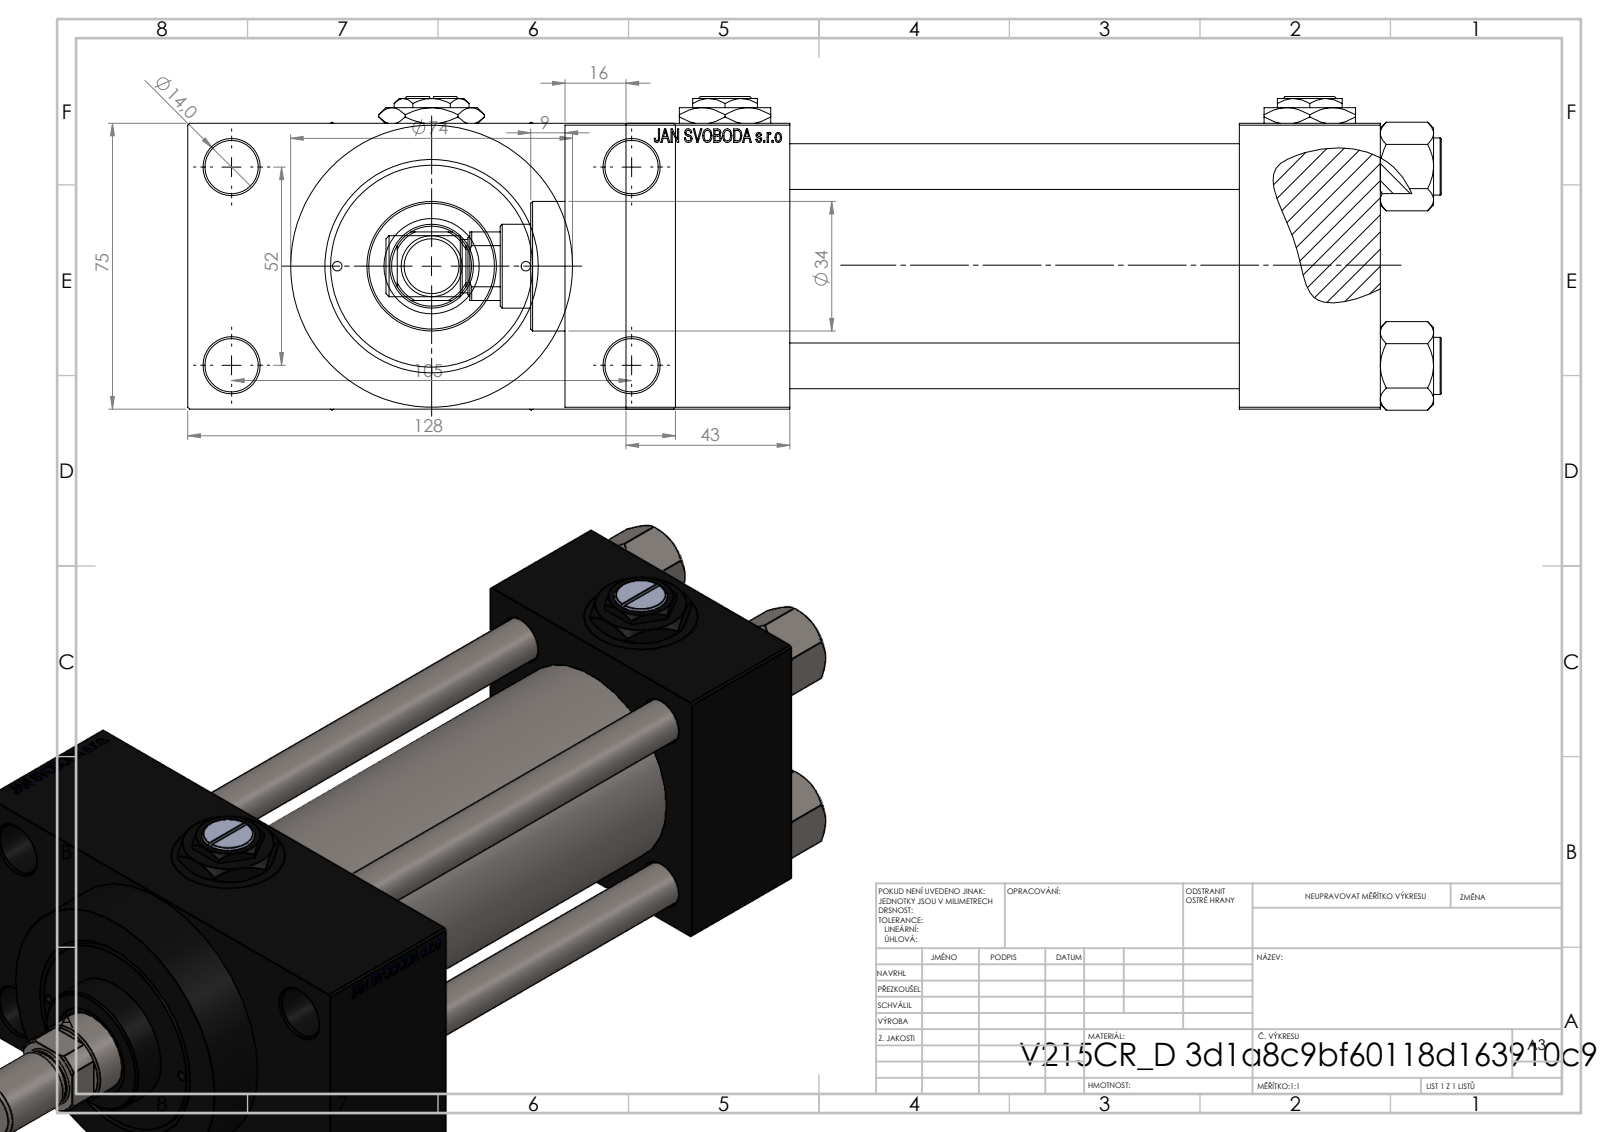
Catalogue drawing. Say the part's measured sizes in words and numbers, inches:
The part is named "ROD_END_AH; NUT_M5_D; V215CR_D_Body; V215CR_D_TYCINKA (+3 more)". Its 3-D file was written by "SolidWorks 2019 (CONFIG_CONTROL_DESIGN)". It is 14 solids with 1226 faces: 551 planar, 107 cylindrical and 568 other. Overall it measures 10.906 by 5.039 by 3.239 inches. Its volume is 53.53 cubic inches and its surface area 318.6 square inches. Round holes: 4 of diameter 0.472, 4 of diameter 0.551, 4 of diameter 0.825, 4 of diameter 1.181, 3 of diameter 0.276, 2 of diameter 0.098, 1 of diameter 0.413, 1 of diameter 0.866, 1 of diameter 0.984, 1 of diameter 1.614, 1 of diameter 1.969, 1 of diameter 2.087. Round bosses or shafts: 4 of diameter 0.591, 1 of diameter 2.913, 1 of diameter 2.205, 1 of diameter 1.339, 1 of diameter 0.63, 1 of diameter 0.551. Partial cylindrical surfaces (rounded edges, fillets, slot ends): 1 of radius 0.413. The main face-to-face distances are 2.953, 4.646, 1.457, 6.102, 1.043, 7.795, 6.339, 1.693, 3.996, 0.63. The hole center spacings are 1.031, 1.037, 1.456, 1.497, 2.059, 2.253, 2.3, 2.307.
